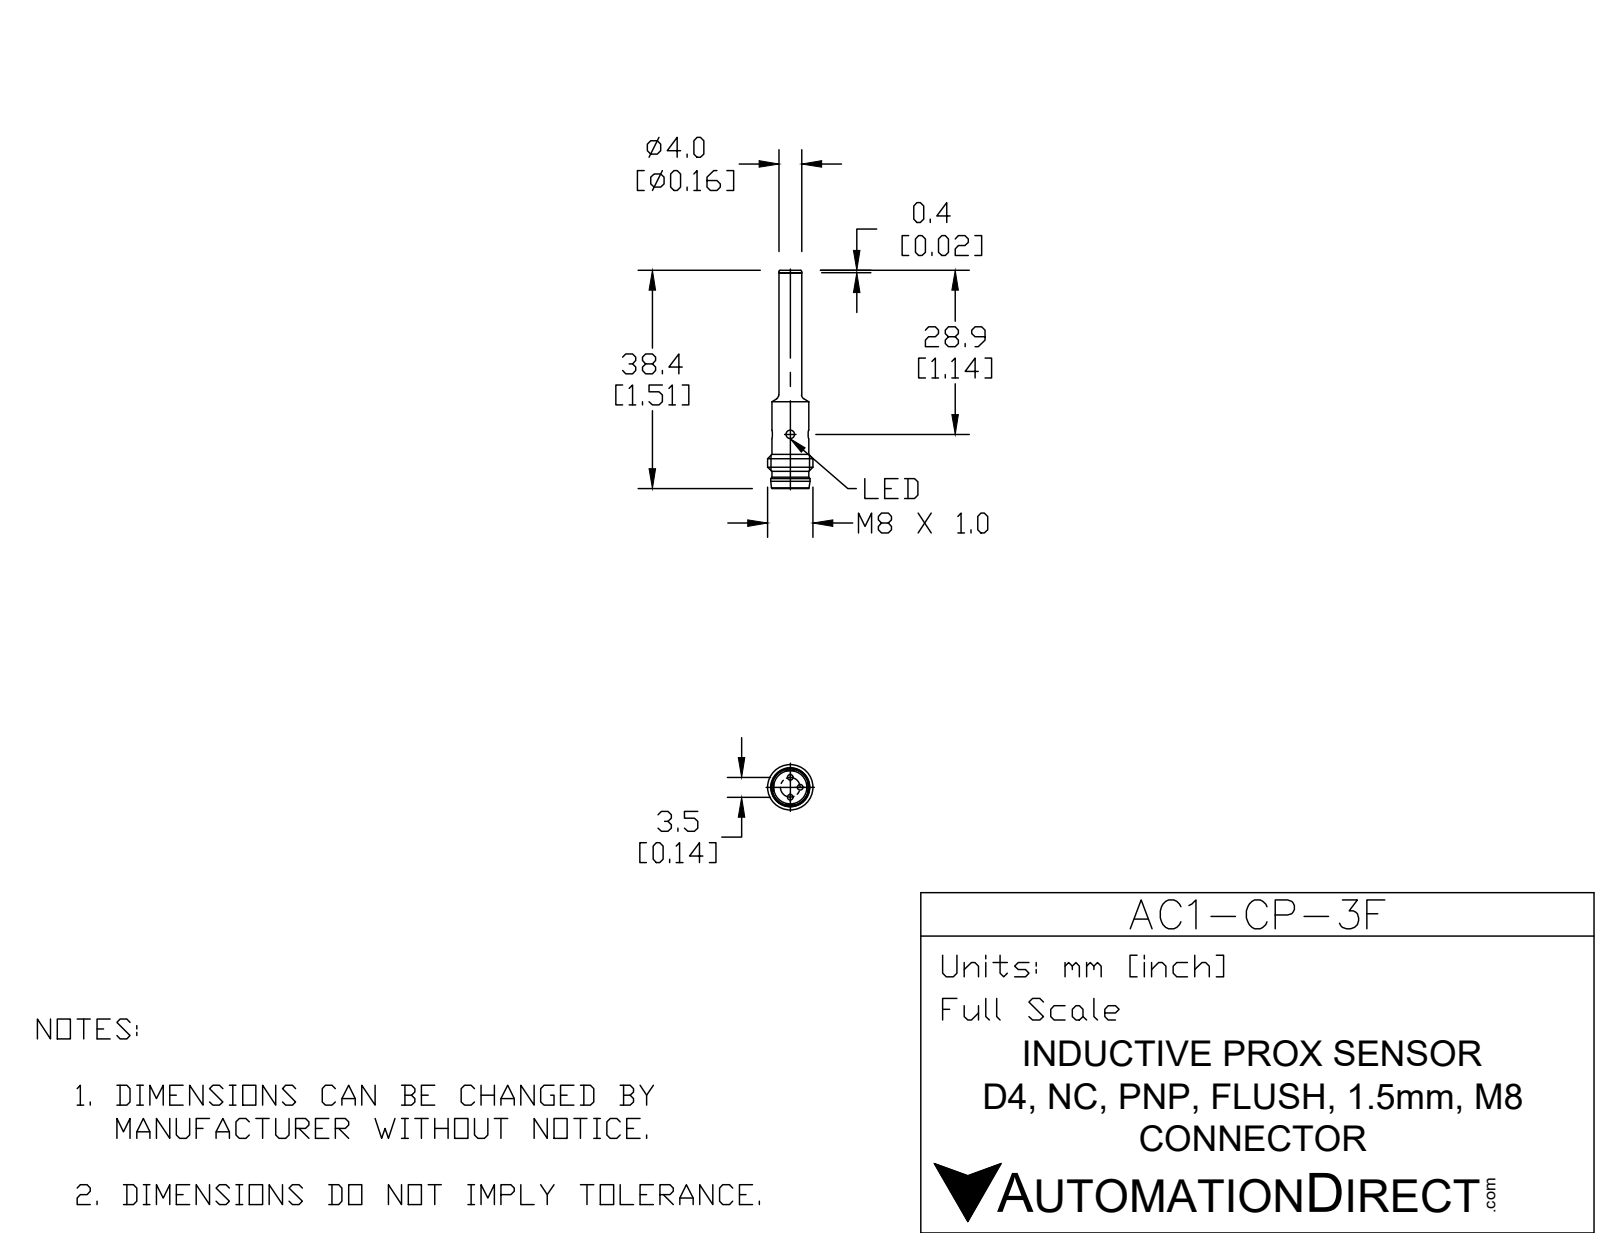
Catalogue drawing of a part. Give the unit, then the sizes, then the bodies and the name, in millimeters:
Units: millimetres
Overall size (bounding box): 38.4 × 8 × 8
Round holes (diameter × count): ⌀1.5 ×2, ⌀5.85 ×1
Round bosses / shafts (diameter × count): ⌀1 ×3, ⌀8 ×1, ⌀6.9 ×1, ⌀6.5 ×1, ⌀4 ×1
Main face-to-face distances: 33.4, 5.5, 5, 38.4, 38, 33, 0.4
Volume: 757 mm³ · Surface area: 840 mm²
Bodies: 4 solids, 59 faces (11 planar, 26 cylindrical, 22 other)
Part name (STEP PRODUCT): AC1-CP-3F
STEP written by: SolidWorks 2015 (CONFIG_CONTROL_DESIGN)
